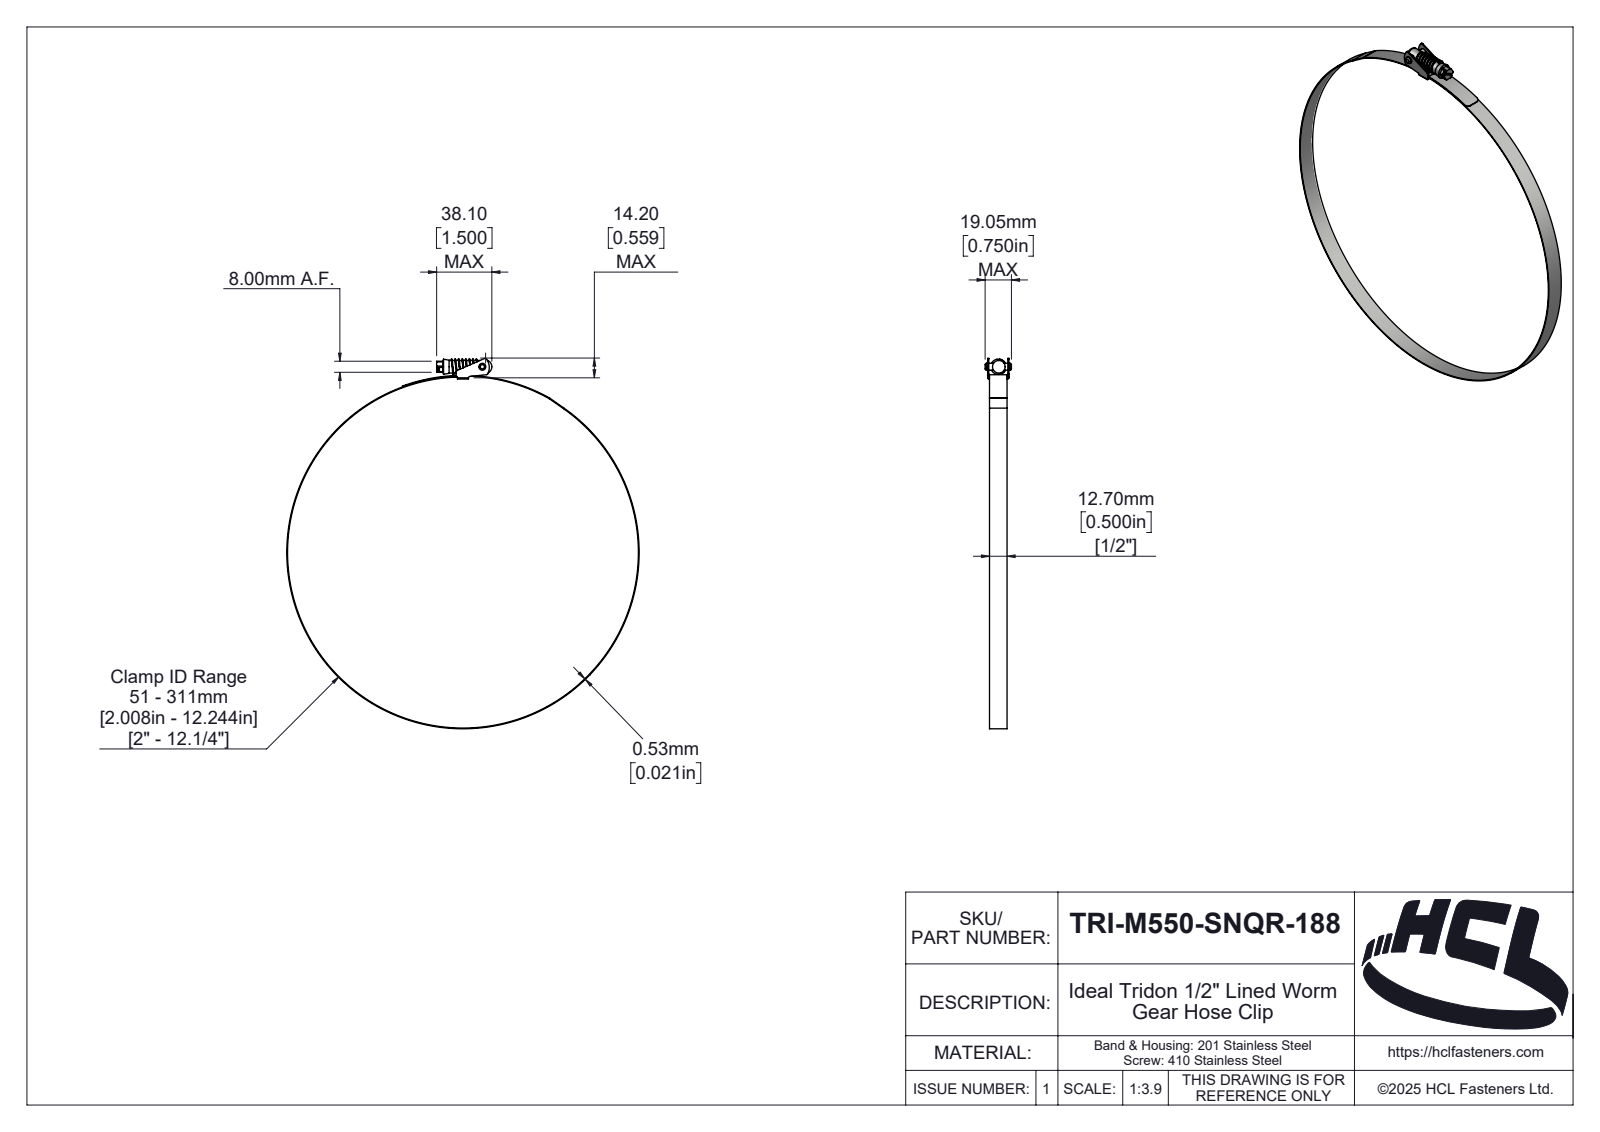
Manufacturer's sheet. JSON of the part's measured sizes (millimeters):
{"part_name": "TRI-M550-SNQR-188", "step_written_by": "SolidWorks 2025 (AUTOMOTIVE_DESIGN)", "units": "millimeters", "bodies": {"solids": 5, "faces": 222, "planar": 44, "cylindrical": 112, "other": 66}, "overall_size": [325.02, 312.06, 19.05], "volume_mm3": 10136, "surface_area_mm2": 30932, "round_holes": [[5, 1], [311, 1]], "round_bosses_or_shafts": [[312.06, 1], [9.1, 1]], "partial_cylinders_radius": [[1, 11], [0.1, 2], [0.9, 2], [3, 2], [0.46, 1], [1.89, 1], [2, 1], [2.35, 1]], "face_to_face_distances": [12.7, 0.8, 1.35, 14.05, 14.6, 0.55, 13.25, 15.4, 13.8, 0.53], "hole_center_spacings": [163.5]}
